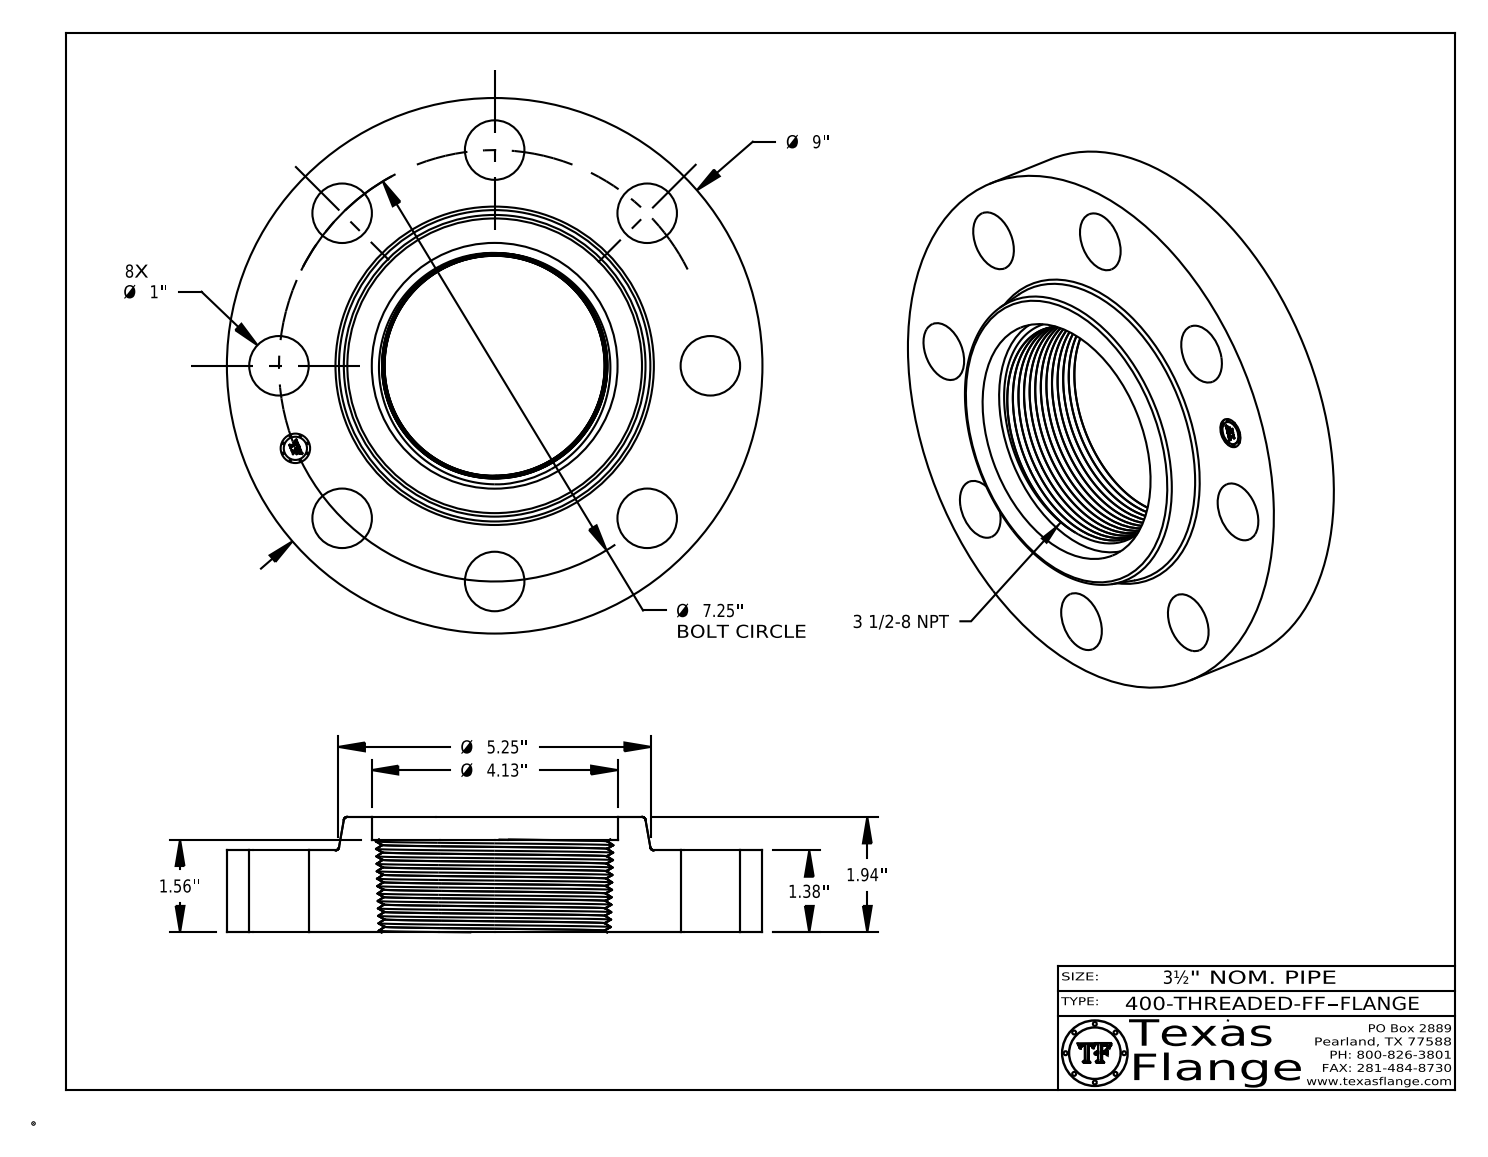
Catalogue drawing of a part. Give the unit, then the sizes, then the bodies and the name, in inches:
Units: inches
Overall size (bounding box): 9 × 9 × 1.94
Round holes (diameter × count): ⌀1 ×8, ⌀0.495 ×1, ⌀4.13 ×1
Round bosses / shafts (diameter × count): ⌀0.03 ×8, ⌀9 ×1, ⌀0.39 ×1
Main face-to-face distances: 1.38, 1.94, 0.56, 1.56, 0.18, 0.38, 1.365, 0.015, 0.195, 0.575
Hole centre spacings: 3.625, 2.774, 5.127, 6.698, 7.25, 1.415, 7.111, 4.028
Volume: 67.63 in³ · Surface area: 212.6 in²
Bodies: 1 solid, 546 faces (369 planar, 40 cylindrical, 137 other)
Part name (STEP PRODUCT): 400-THREADED-FF
STEP written by: CATIA V5 STEP AP214 (AUTOMOTIVE_DESIGN)
